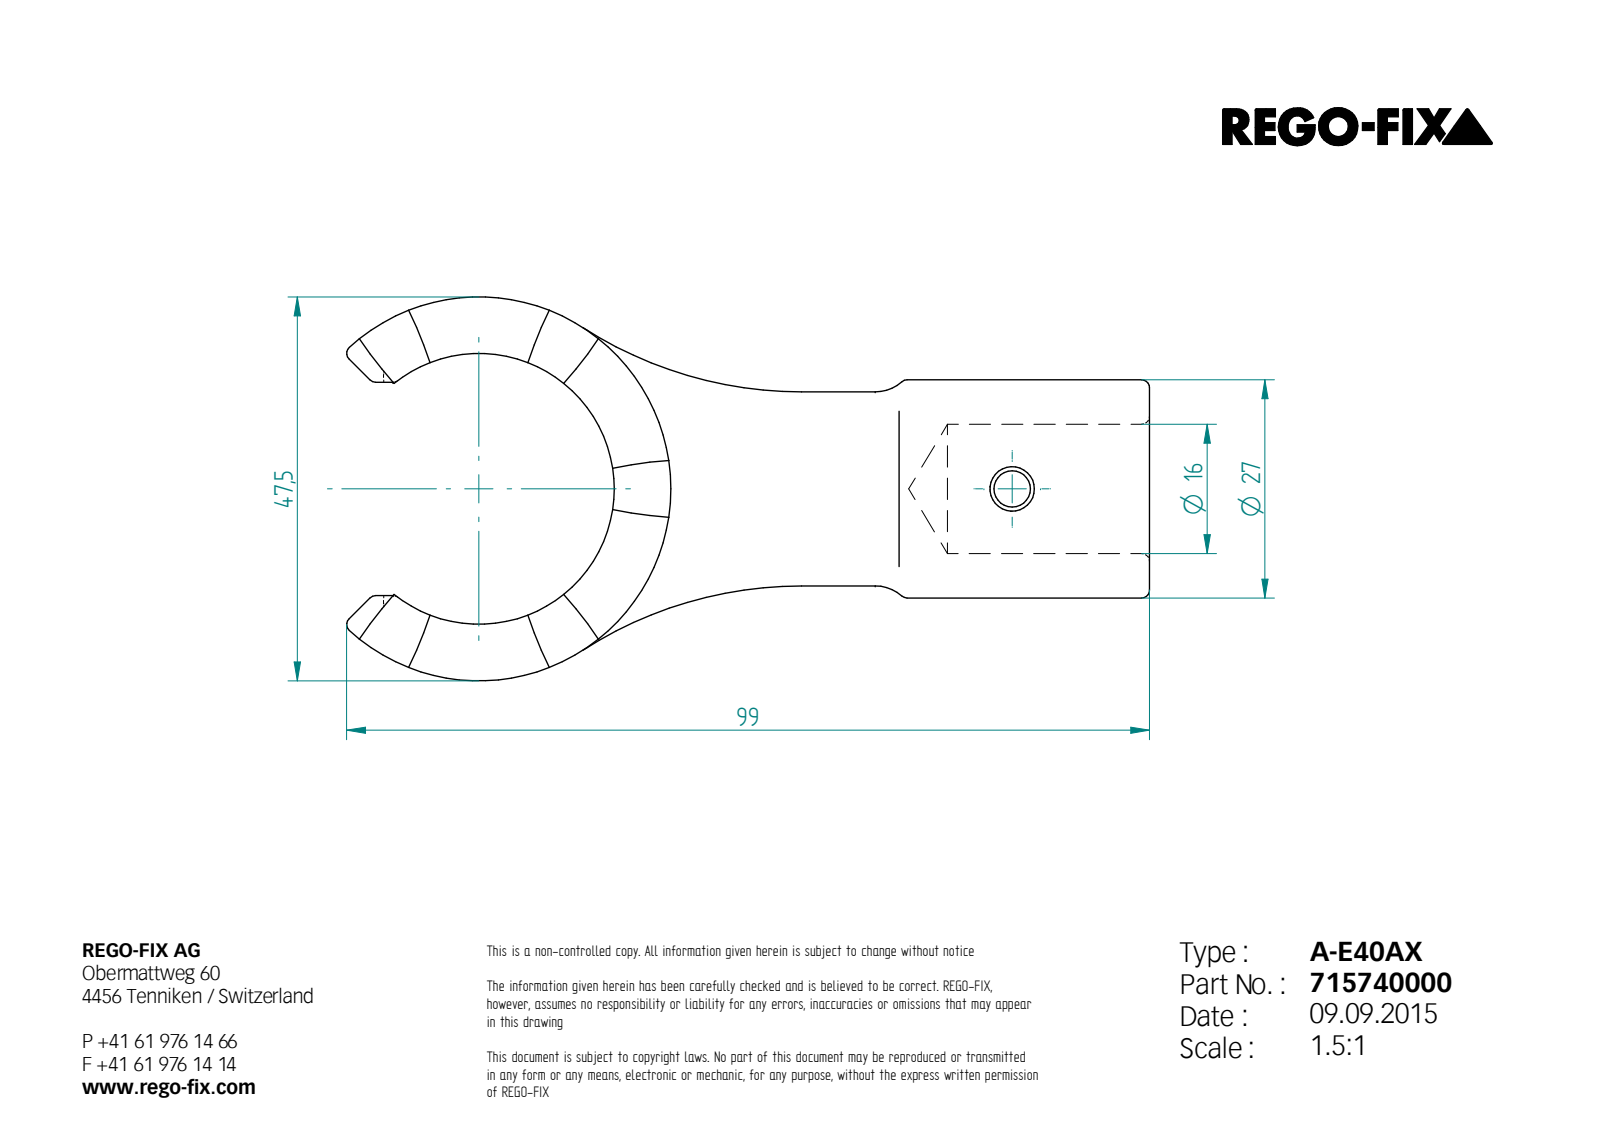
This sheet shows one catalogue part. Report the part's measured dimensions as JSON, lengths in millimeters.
{"step_written_by": "Unknown (AUTOMOTIVE_DESIGN)", "units": "millimeters", "bodies": {"solids": 1, "faces": 88, "planar": 24, "cylindrical": 33, "other": 31}, "overall_size": [99.36, 47.5, 27], "volume_mm3": 25152, "surface_area_mm2": 10308, "round_holes": [[4.5, 1], [5.5, 1], [16, 1]], "round_bosses_or_shafts": [[27, 1]], "partial_cylinders_radius": [[1, 6], [2, 6], [50.04, 6], [5, 2], [50, 2], [16.75, 1], [23.75, 1]], "face_to_face_distances": [6, 12, 14, 8, 2, 31, 1.2, 25.2, 26.4, 24]}
